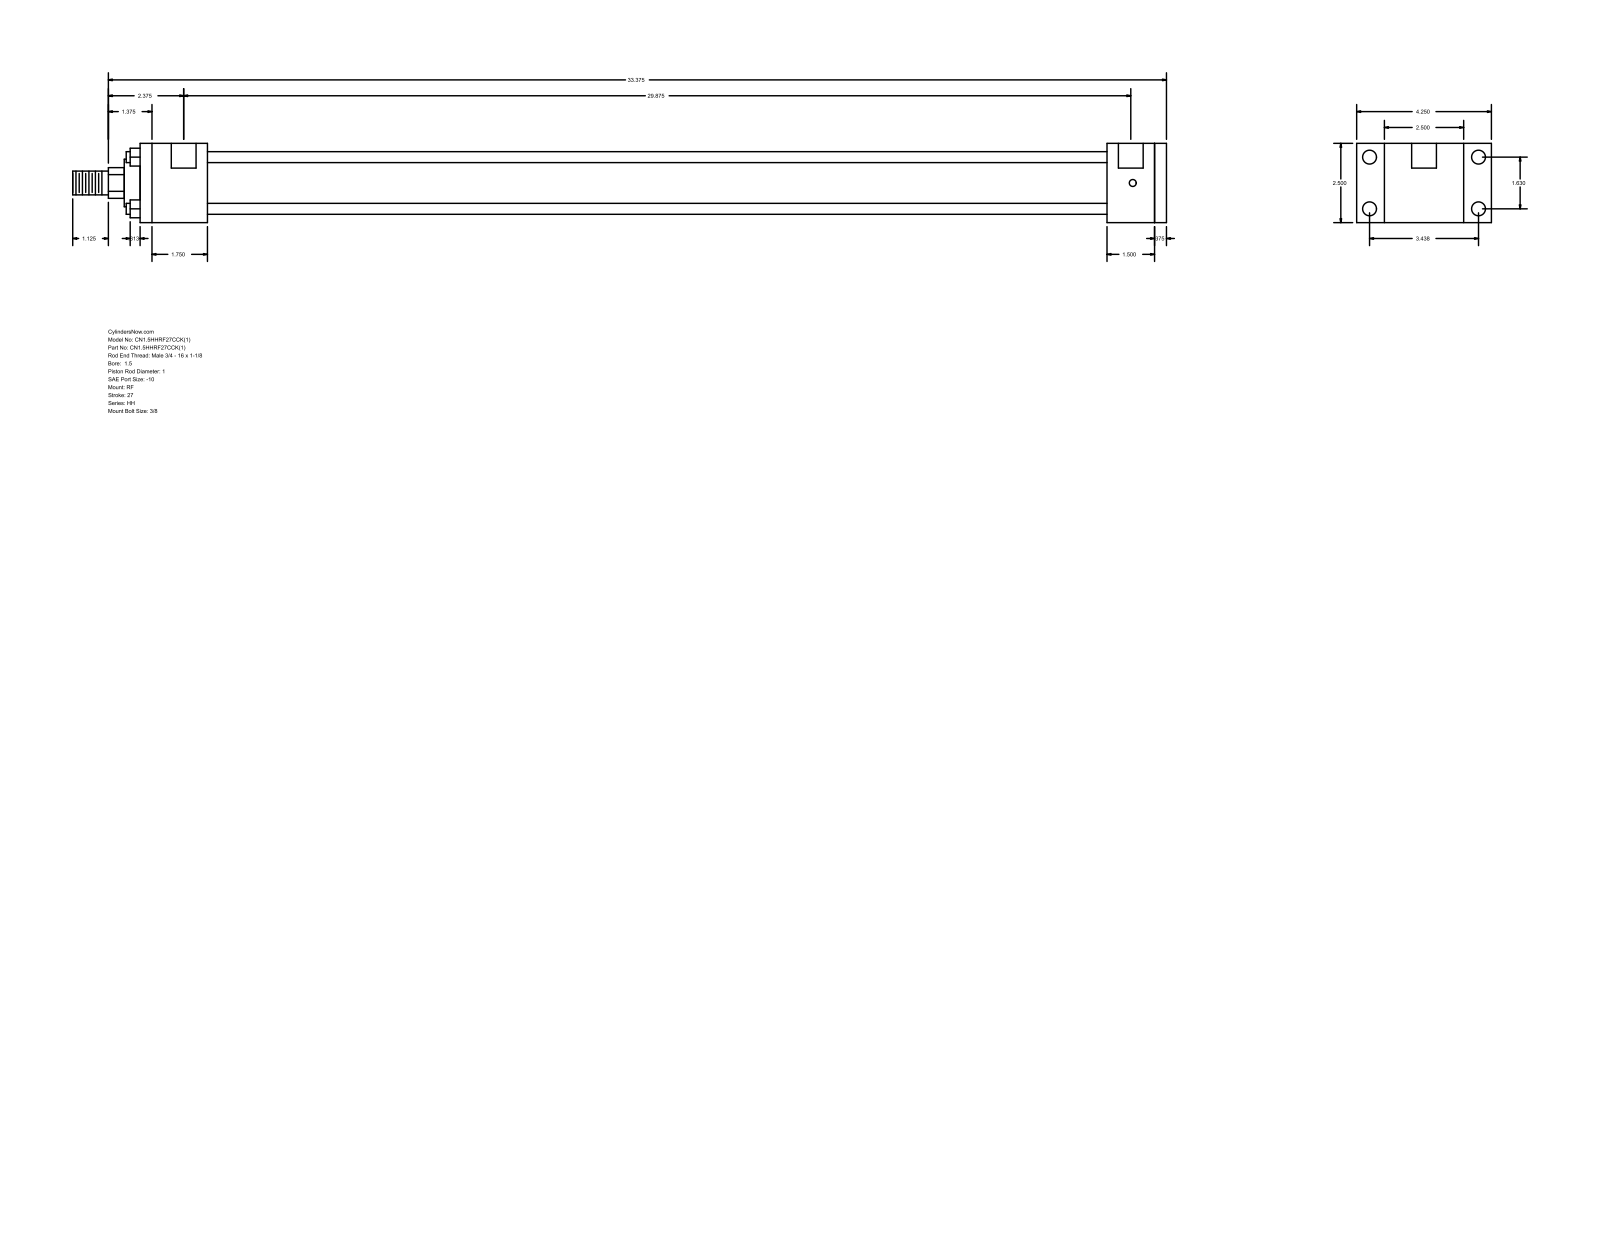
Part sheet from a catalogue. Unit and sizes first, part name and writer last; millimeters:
Units: millimetres
Overall size (bounding box): 876.3 × 107.95 × 63.5
Round holes (diameter × count): ⌀5.56 ×4, ⌀11.13 ×4, ⌀19.84 ×2
Round bosses / shafts (diameter × count): ⌀8.76 ×4, ⌀44.45 ×1, ⌀38.1 ×1, ⌀25.4 ×1, ⌀19.05 ×1
Partial cylindrical surfaces — rounded edges, fillets, slot ends (radius × count): R12.29 ×1
Main face-to-face distances: 63.5, 9.53, 38.1, 720.72, 758.82, 768.35, 47.63, 53.98, 774.7, 812.8
Hole centre spacings: 1.59, 41.4, 87.32, 96.64, 760.41, 762, 758.82
Bodies: 0 solids, 92 faces (64 planar, 28 cylindrical, 0 other)
Part name (STEP PRODUCT): HH_RF__0150_1
STEP written by: GSSL Pune (CONFIG_CONTROL_DESIGN)
